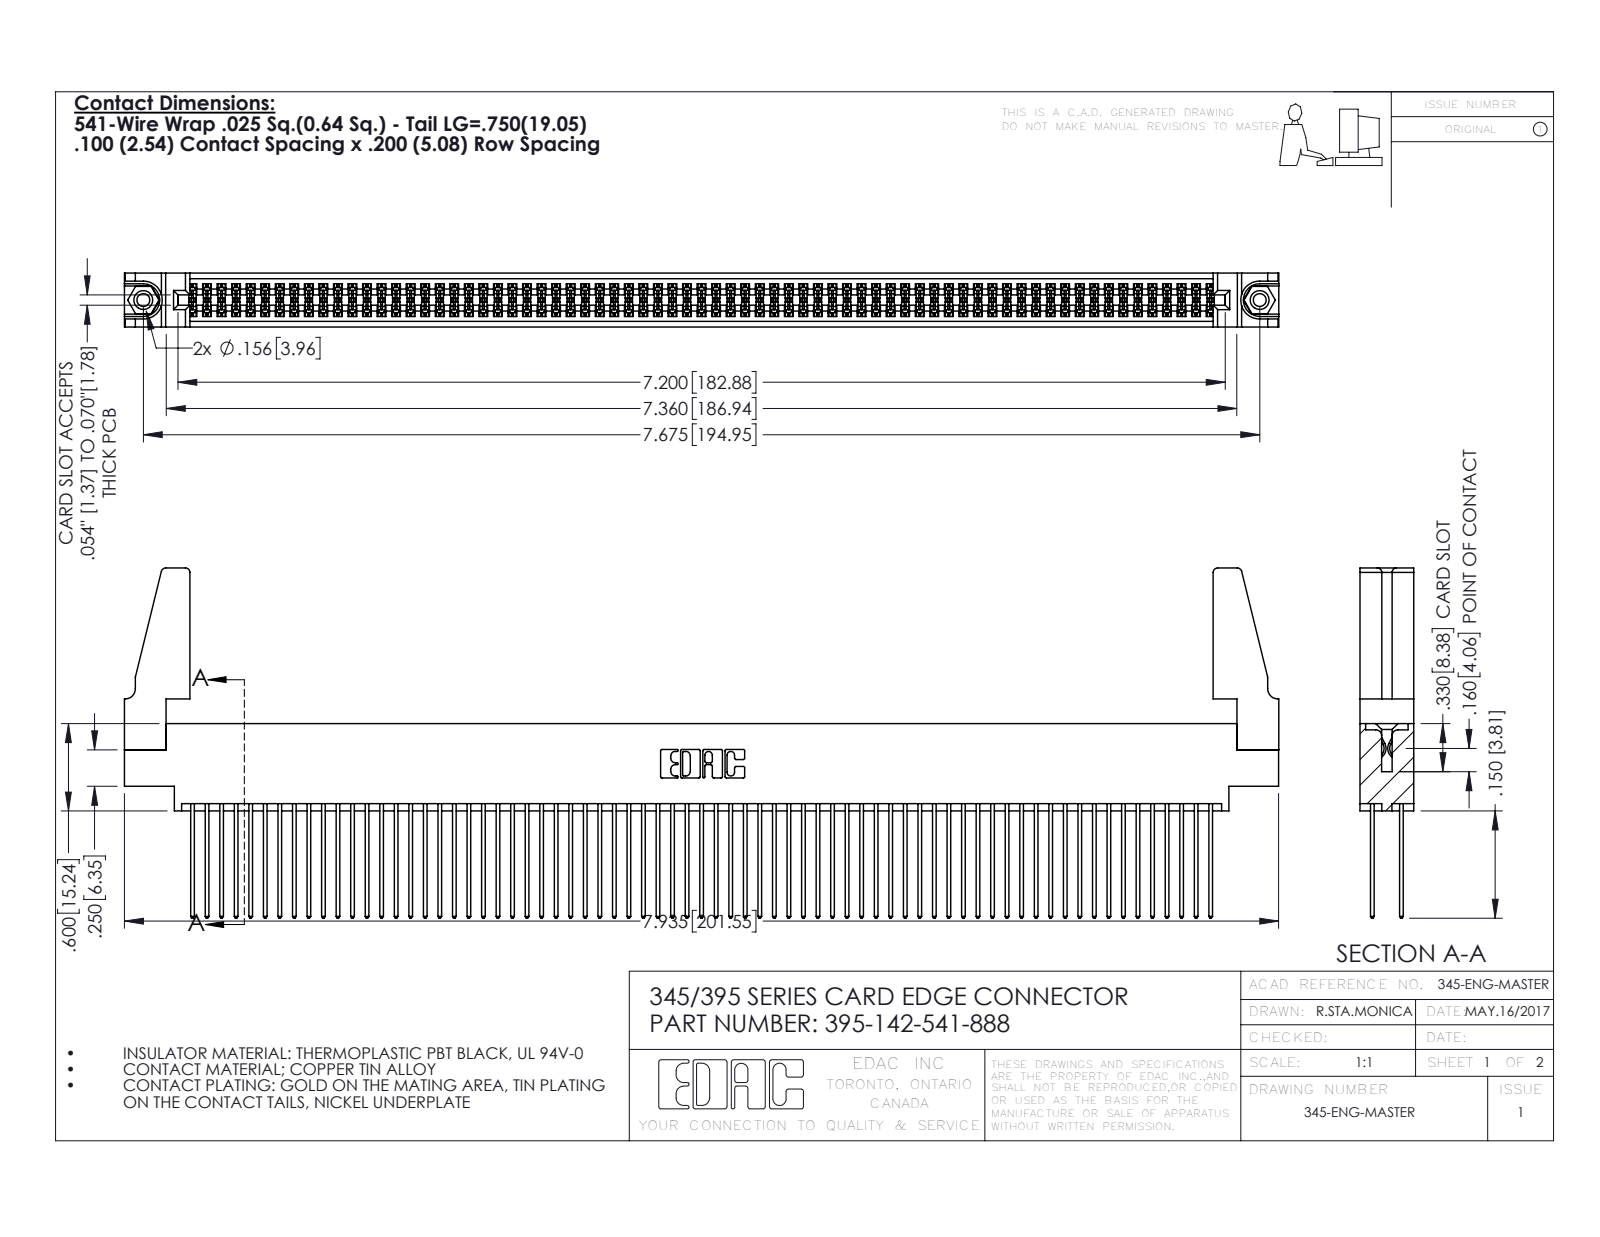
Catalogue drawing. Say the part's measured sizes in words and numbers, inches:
The part is named "345-220-078_345-220-088; 395-142-541-888; 345 Part_0.170 Offset - 0.156 Dia-TH; 345-292-001_345-293-141 (+1 more)". Its 3-D file was written by "SolidWorks 2016 (CONFIG_CONTROL_DESIGN)". It is 147 solids with 7354 faces: 4842 planar, 2496 cylindrical and 16 other. Overall it measures 7.936 by 2.407 by 0.37 inches. Its volume is 1.453 cubic inches and its surface area 58.96 square inches. Round holes: 2 of diameter 0.089, 2 of diameter 0.125, 2 of diameter 0.156, 1 of diameter 0.064. Round bosses or shafts: 2 of diameter 0.155. Partial cylindrical surfaces (rounded edges, fillets, slot ends): 213 of radius 0.006, 142 of radius 0.01, 22 of radius 0.01, 8 of radius 0.03, 6 of radius 0.007, 6 of radius 0.031, 3 of radius 0.026, 2 of radius 0.014. The main face-to-face distances are 0.072, 0.298, 0.098, 0.272, 0.025, 0.2, 0.37, 0.225, 0.175, 0.149. The hole center spacings are 0.27, 7.439, 7.675.
